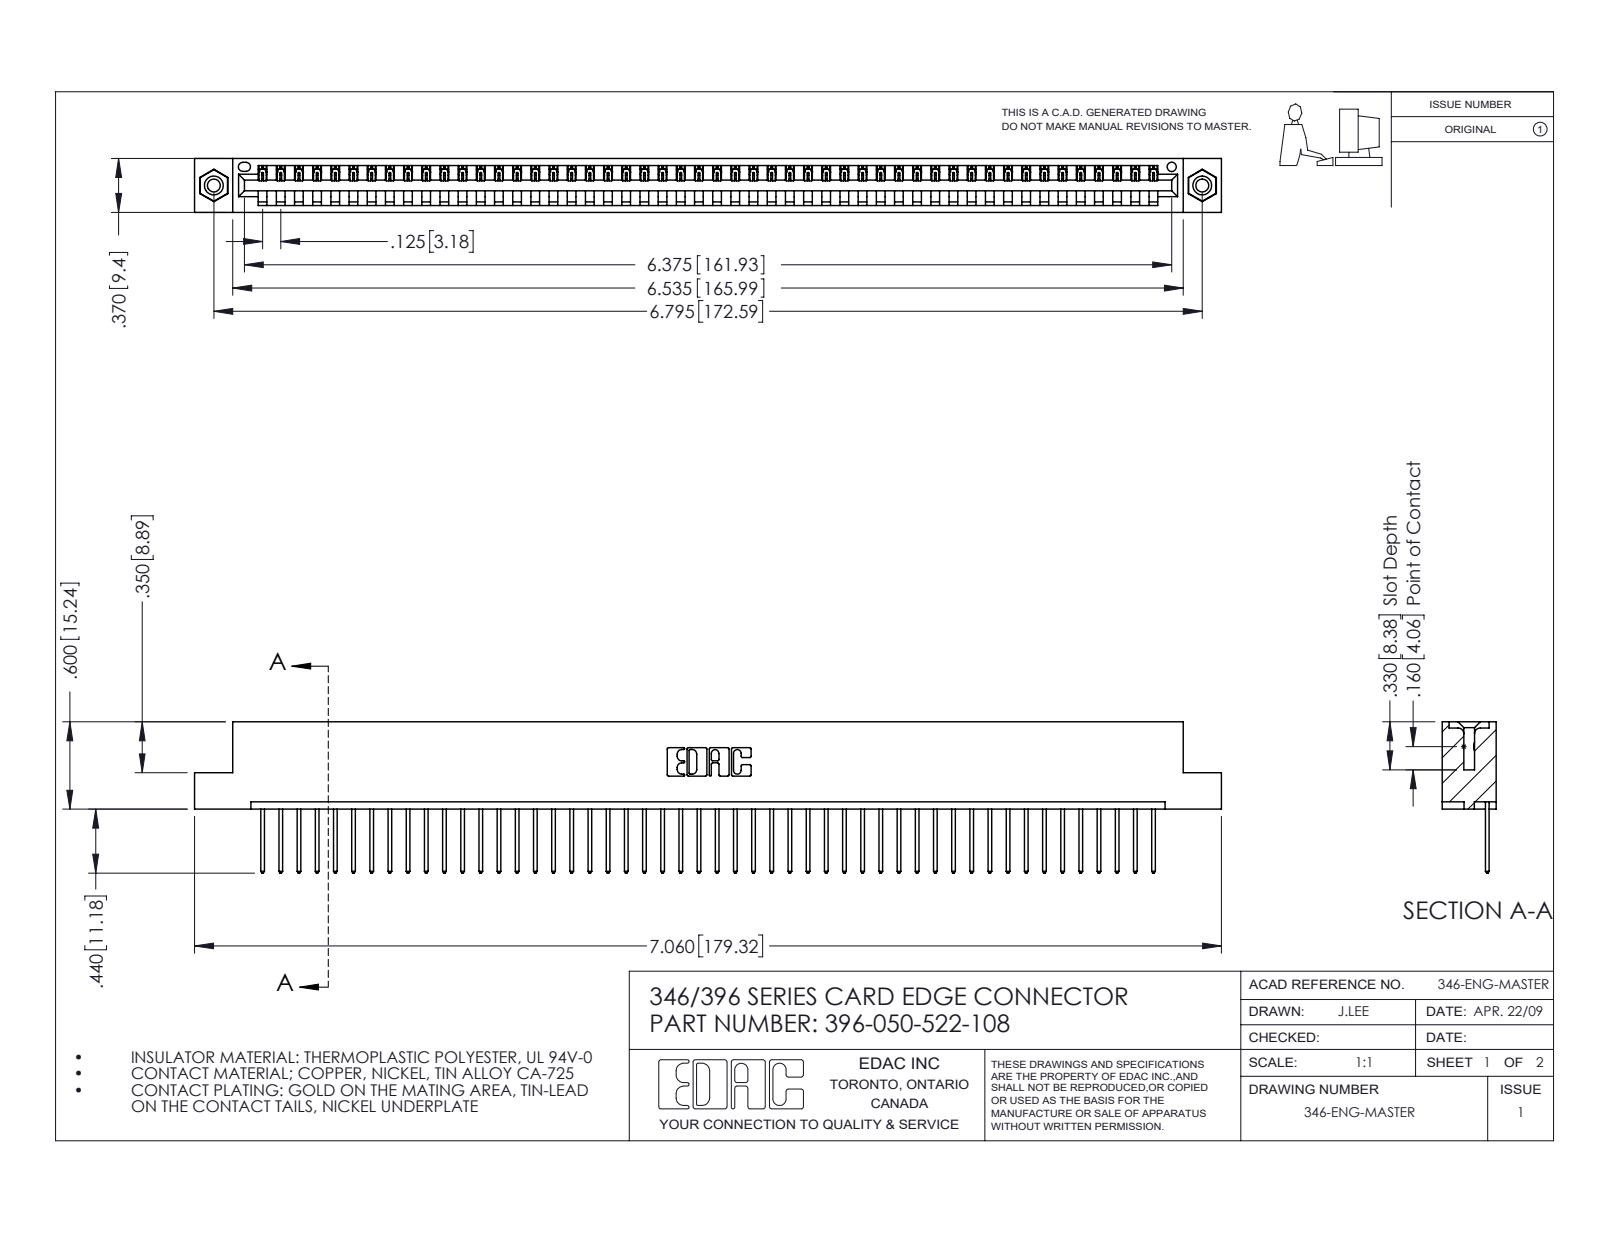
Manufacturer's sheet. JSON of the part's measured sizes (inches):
{"part_name": "345-292-001_345-293-122; 396-050-522-108; 345-250-001_345-250-003-102; 346 Part_Flush Mounting Lugs - 0.156 Dia-TI", "step_written_by": "SolidWorks 2016 (CONFIG_CONTROL_DESIGN)", "units": "inches", "bodies": {"solids": 53, "faces": 3082, "planar": 2108, "cylindrical": 958, "other": 16}, "overall_size": [7.06, 1.04, 0.37], "volume_in3": 1.051, "surface_area_in2": 33.81, "round_holes": [[0.089, 2], [0.125, 2], [0.156, 2], [0.064, 1]], "round_bosses_or_shafts": [[0.155, 2]], "partial_cylinders_radius": [[0.006, 100], [0.01, 100], [0.01, 22], [0.007, 6], [0.031, 6], [0.026, 3], [0.031, 2], [0.04, 2]], "face_to_face_distances": [0.048, 0.322, 0.37, 0.25, 0.072, 0.298, 0.025, 0.148, 0.222, 0.1], "hole_center_spacings": [0.246, 6.586, 6.795]}
